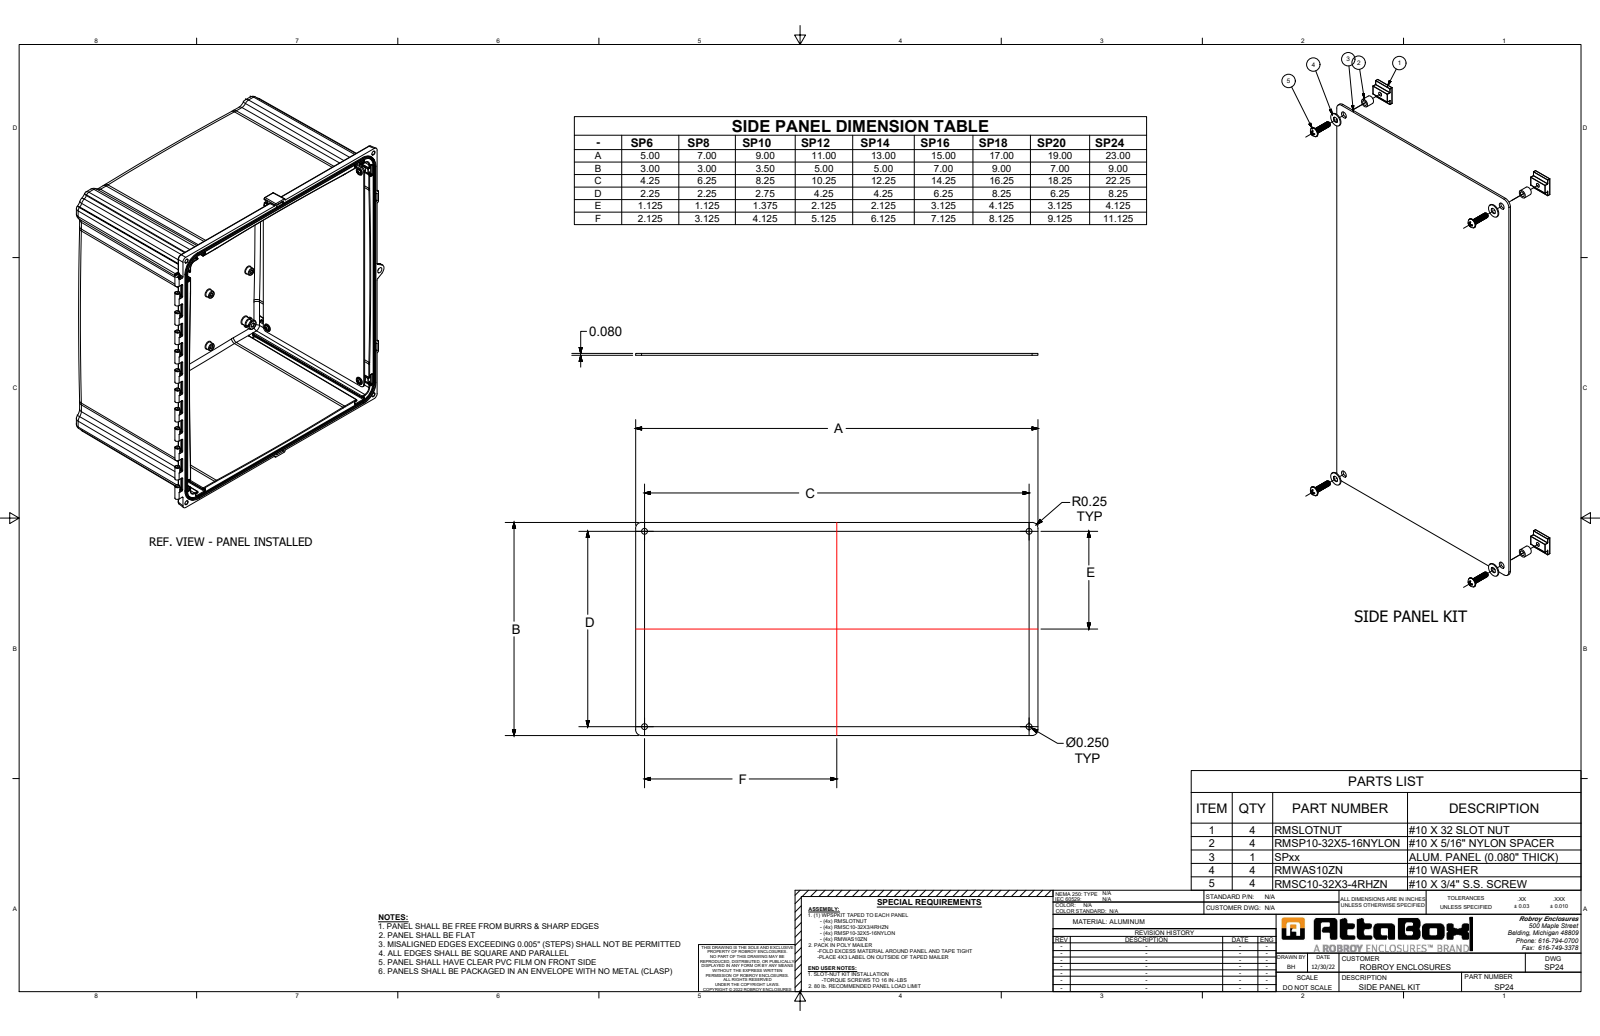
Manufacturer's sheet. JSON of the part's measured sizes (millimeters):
{"part_name": "SP24_Default", "step_written_by": "SolidWorks 2023 (CONFIG_CONTROL_DESIGN)", "units": "millimeters", "bodies": {"solids": 1, "faces": 14, "planar": 6, "cylindrical": 8, "other": 0}, "overall_size": [584.2, 228.6, 2], "volume_mm3": 271000, "surface_area_mm2": 270200, "round_holes": [[6.4, 4]], "partial_cylinders_radius": [[6.4, 4]], "face_to_face_distances": [2, 228.6, 584.2], "hole_center_spacings": [209.6, 565.2, 602.7]}
